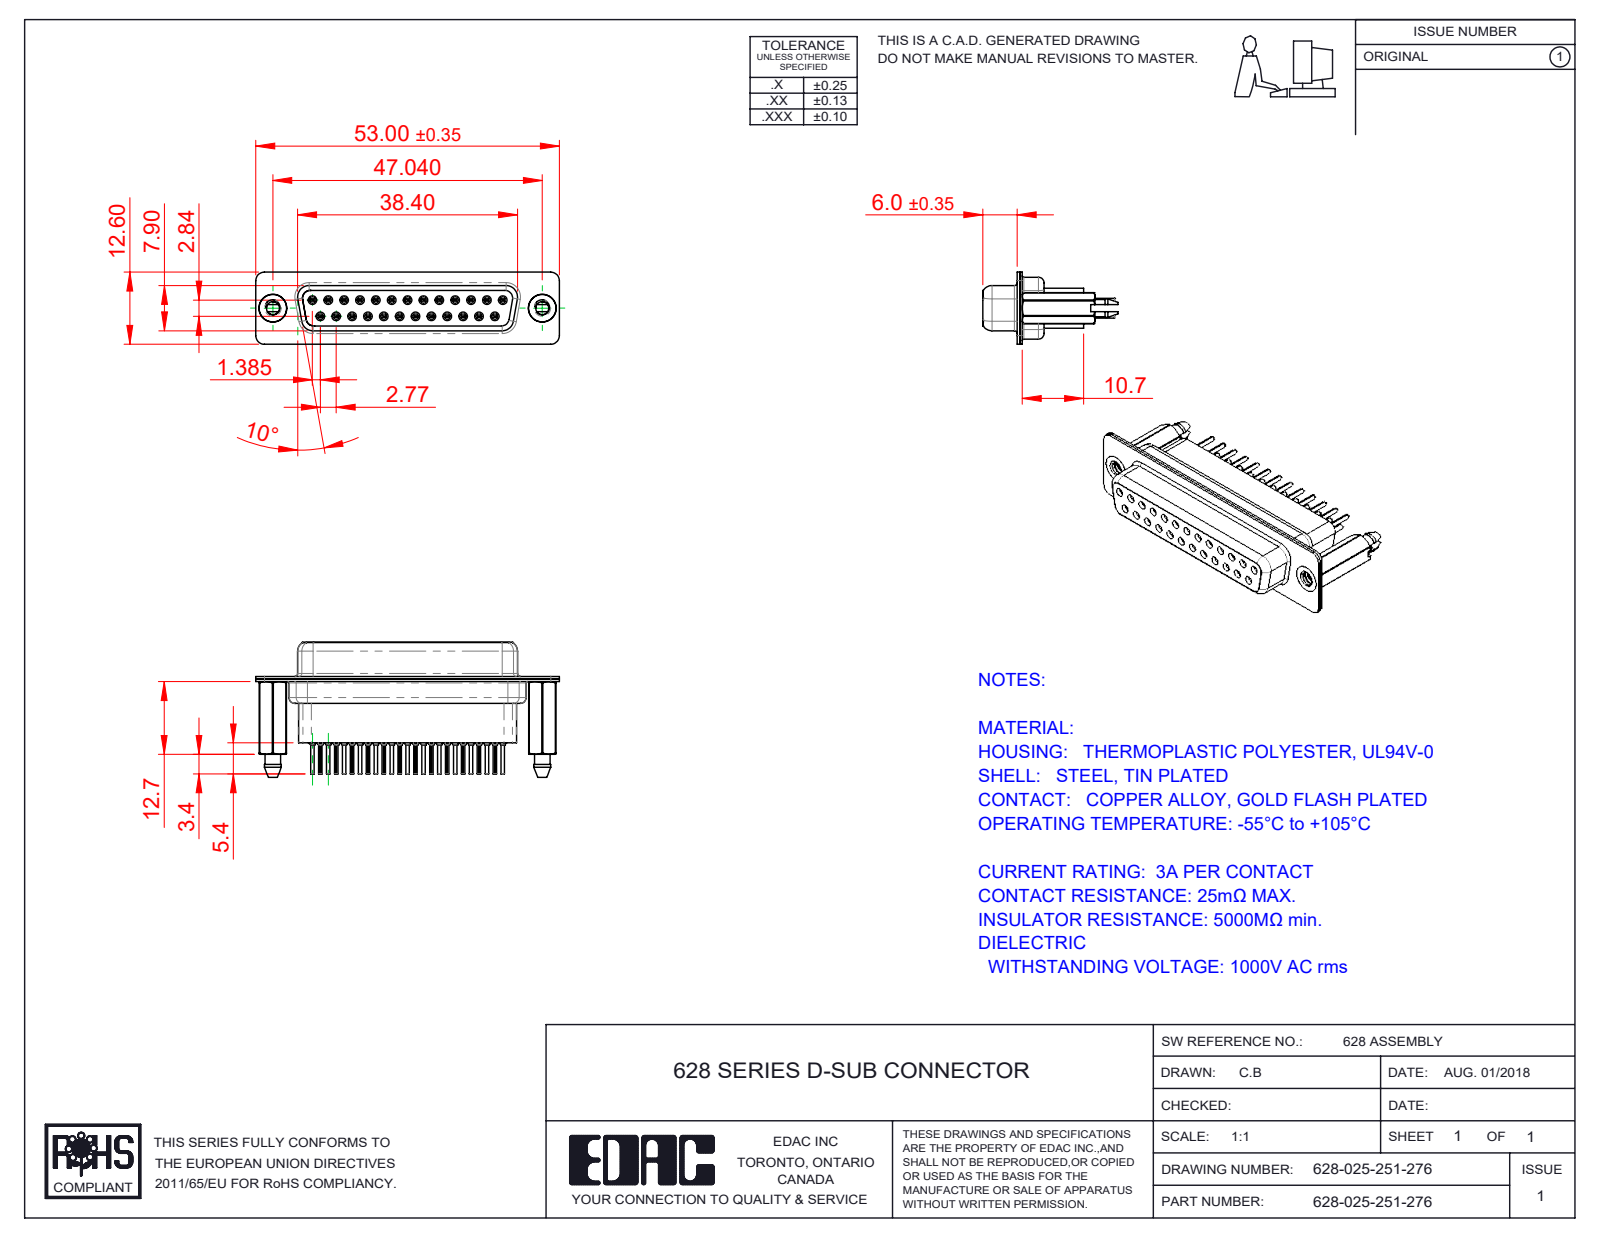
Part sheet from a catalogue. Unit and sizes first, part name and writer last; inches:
Units: inches
Overall size (bounding box): 2.087 × 0.929 × 0.496
Round holes (diameter × count): ⌀0.008 ×25, ⌀0.031 ×25, ⌀0.035 ×25, ⌀0.043 ×25, ⌀0.063 ×25, ⌀0.067 ×13, ⌀0.089 ×2, ⌀0.157 ×2, ⌀0.159 ×2, ⌀0.191 ×2
Round bosses / shafts (diameter × count): ⌀0.079 ×25, ⌀0.059 ×25, ⌀0.047 ×25, ⌀0.024 ×25, ⌀0.195 ×2, ⌀0.189 ×2
Partial cylindrical surfaces — rounded edges, fillets, slot ends (radius × count): R0.004 ×50, R0.011 ×25, R0.059 ×18, R0.079 ×12, R0.053 ×6, R0.063 ×6, R0.01 ×4, R0.02 ×4
Main face-to-face distances: 0.018, 0.016, 0.26, 0.335, 0.075, 0.276, 0.035, 0.055, 0.278, 0.033
Hole centre spacings: 0.124, 0.327, 0.109, 0.218, 0.436, 0.654, 0.198, 0.198
Volume: 0.324 in³ · Surface area: 18.86 in²
Bodies: 30 solids, 3428 faces (874 planar, 994 cylindrical, 1560 other)
Part name (STEP PRODUCT): 628 Housing_25 HP; 628-025-251-276; 628 Contact Row 1_51; 628 Contact Row 2_51 (+3 more)
STEP written by: SolidWorks 2020 (CONFIG_CONTROL_DESIGN)
